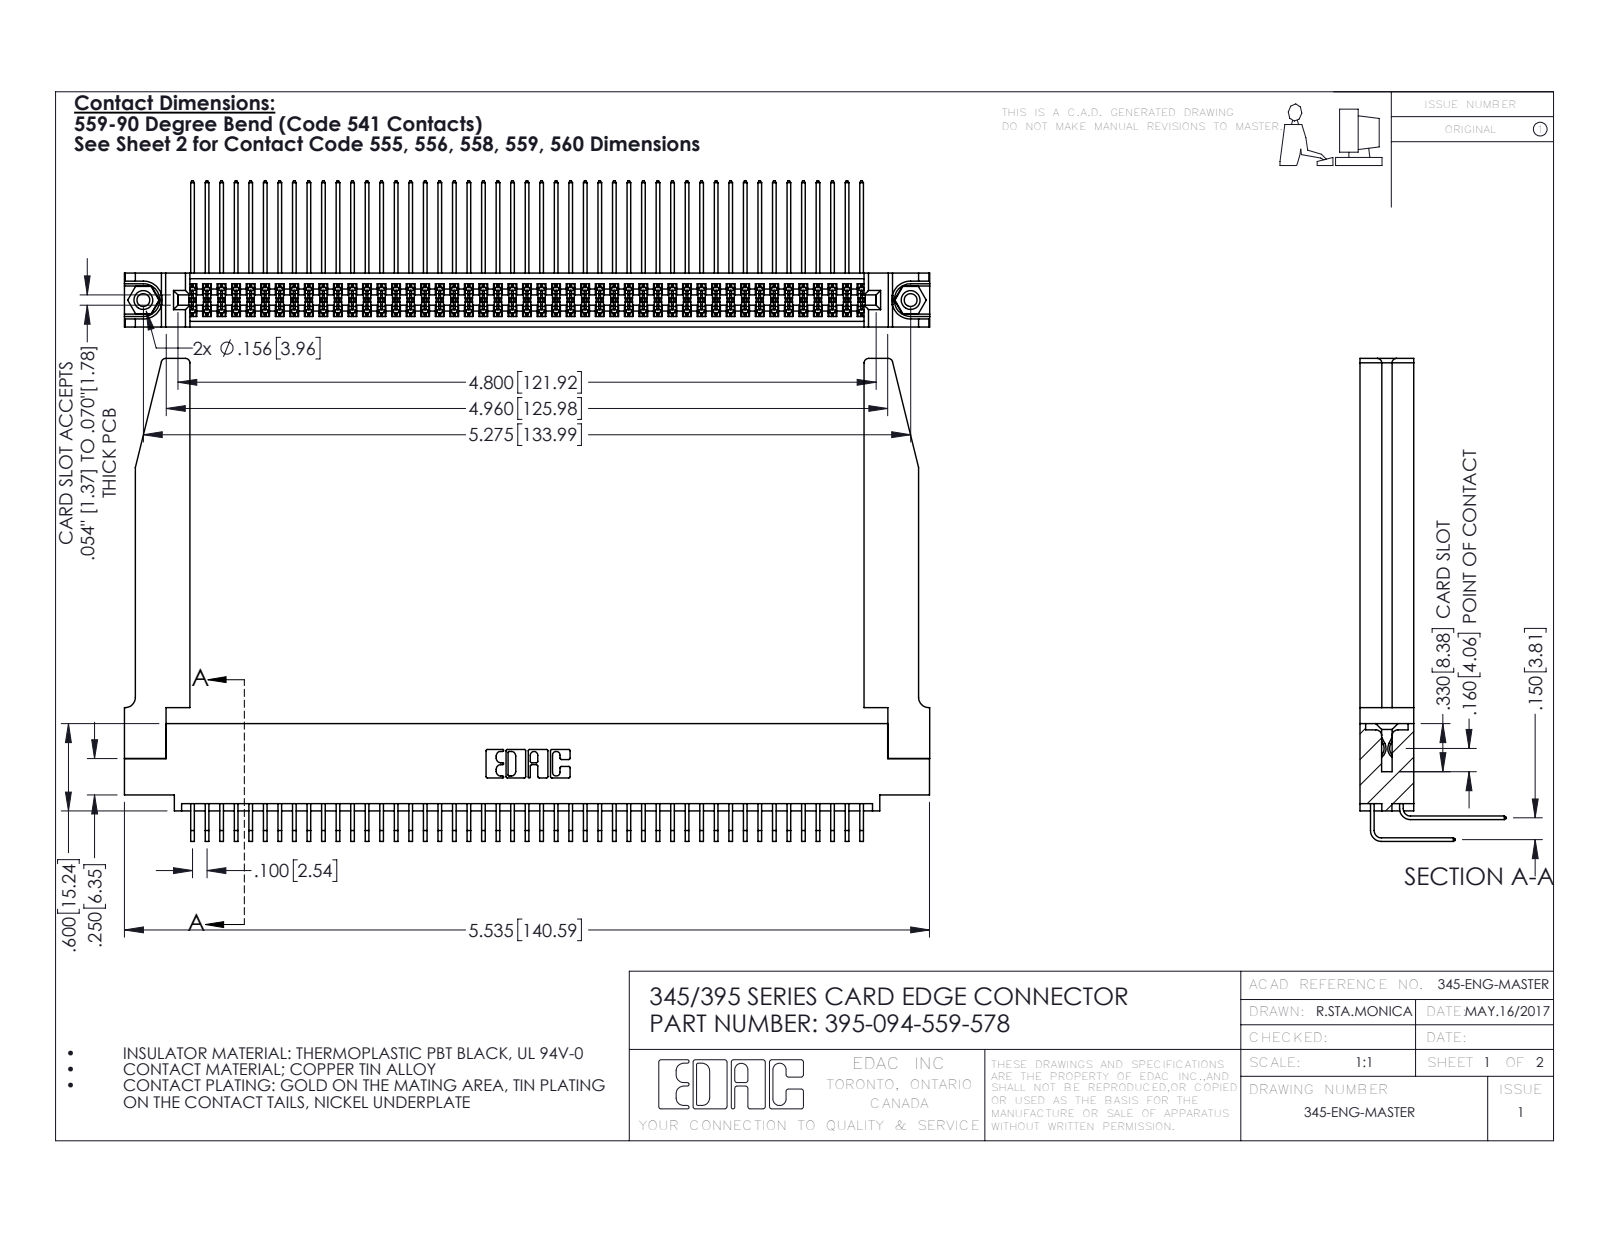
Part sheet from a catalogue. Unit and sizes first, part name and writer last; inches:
Units: inches
Overall size (bounding box): 5.536 × 3.319 × 1.005
Round holes (diameter × count): ⌀0.089 ×2, ⌀0.125 ×2, ⌀0.156 ×2, ⌀0.064 ×1
Round bosses / shafts (diameter × count): ⌀0.155 ×2
Partial cylindrical surfaces — rounded edges, fillets, slot ends (radius × count): R0.006 ×141, R0.01 ×22, R0.03 ×8, R0.007 ×6, R0.031 ×6, R0.026 ×3, R0.014 ×2, R0.019 ×2
Main face-to-face distances: 0.072, 0.37, 0.298, 0.098, 0.272, 0.025, 0.2, 0.225, 0.175, 0.15
Hole centre spacings: 0.27, 5.039, 5.275
Volume: 1.339 in³ · Surface area: 47.32 in²
Bodies: 99 solids, 5252 faces (3516 planar, 1684 cylindrical, 52 other)
Part name (STEP PRODUCT): 345-220-078_345-220-078; 345-250-001_345-250-001-102; 345-292-001_558 559 Tail - 1; 345 Part_0.110 Offset - 0.156 Dia-TH (+2 more)
STEP written by: SolidWorks 2016 (CONFIG_CONTROL_DESIGN)
